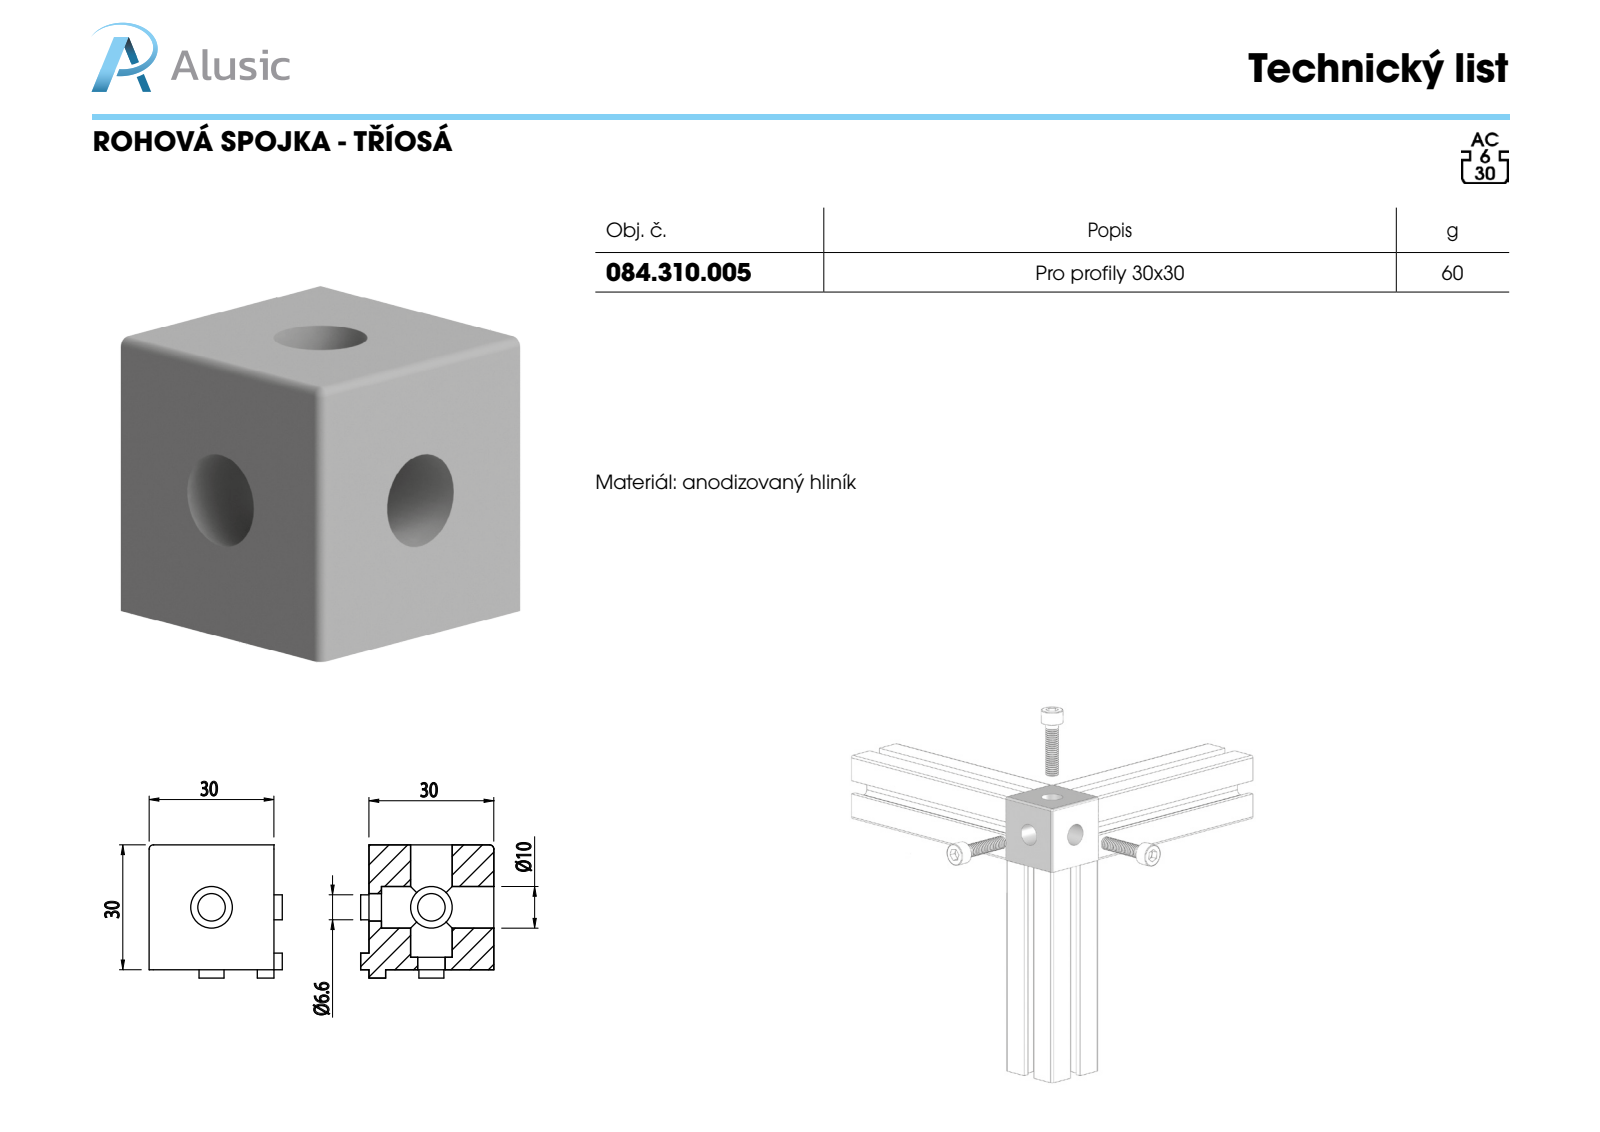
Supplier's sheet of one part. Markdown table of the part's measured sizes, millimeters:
| quantity | value |
| --- | --- |
| part name | 084.310.005 |
| STEP written by | SolidWorks 2011 (CONFIG_CONTROL_DESIGN) |
| units | millimeters |
| bodies | 1 solid, 61 faces (39 planar, 21 cylindrical, 1 other) |
| overall size | 32 × 32 × 32 |
| volume | 22 013 mm³ |
| surface area | 7 278 mm² |
| round holes (diameter × count) | 6.6 × 3, 10 × 3 |
| partial cylindrical surfaces (radius × count) | 1 × 3 |
| main face-to-face distances | 30, 2, 32, 5, 3, 27, 6, 14, 12, 18 |
